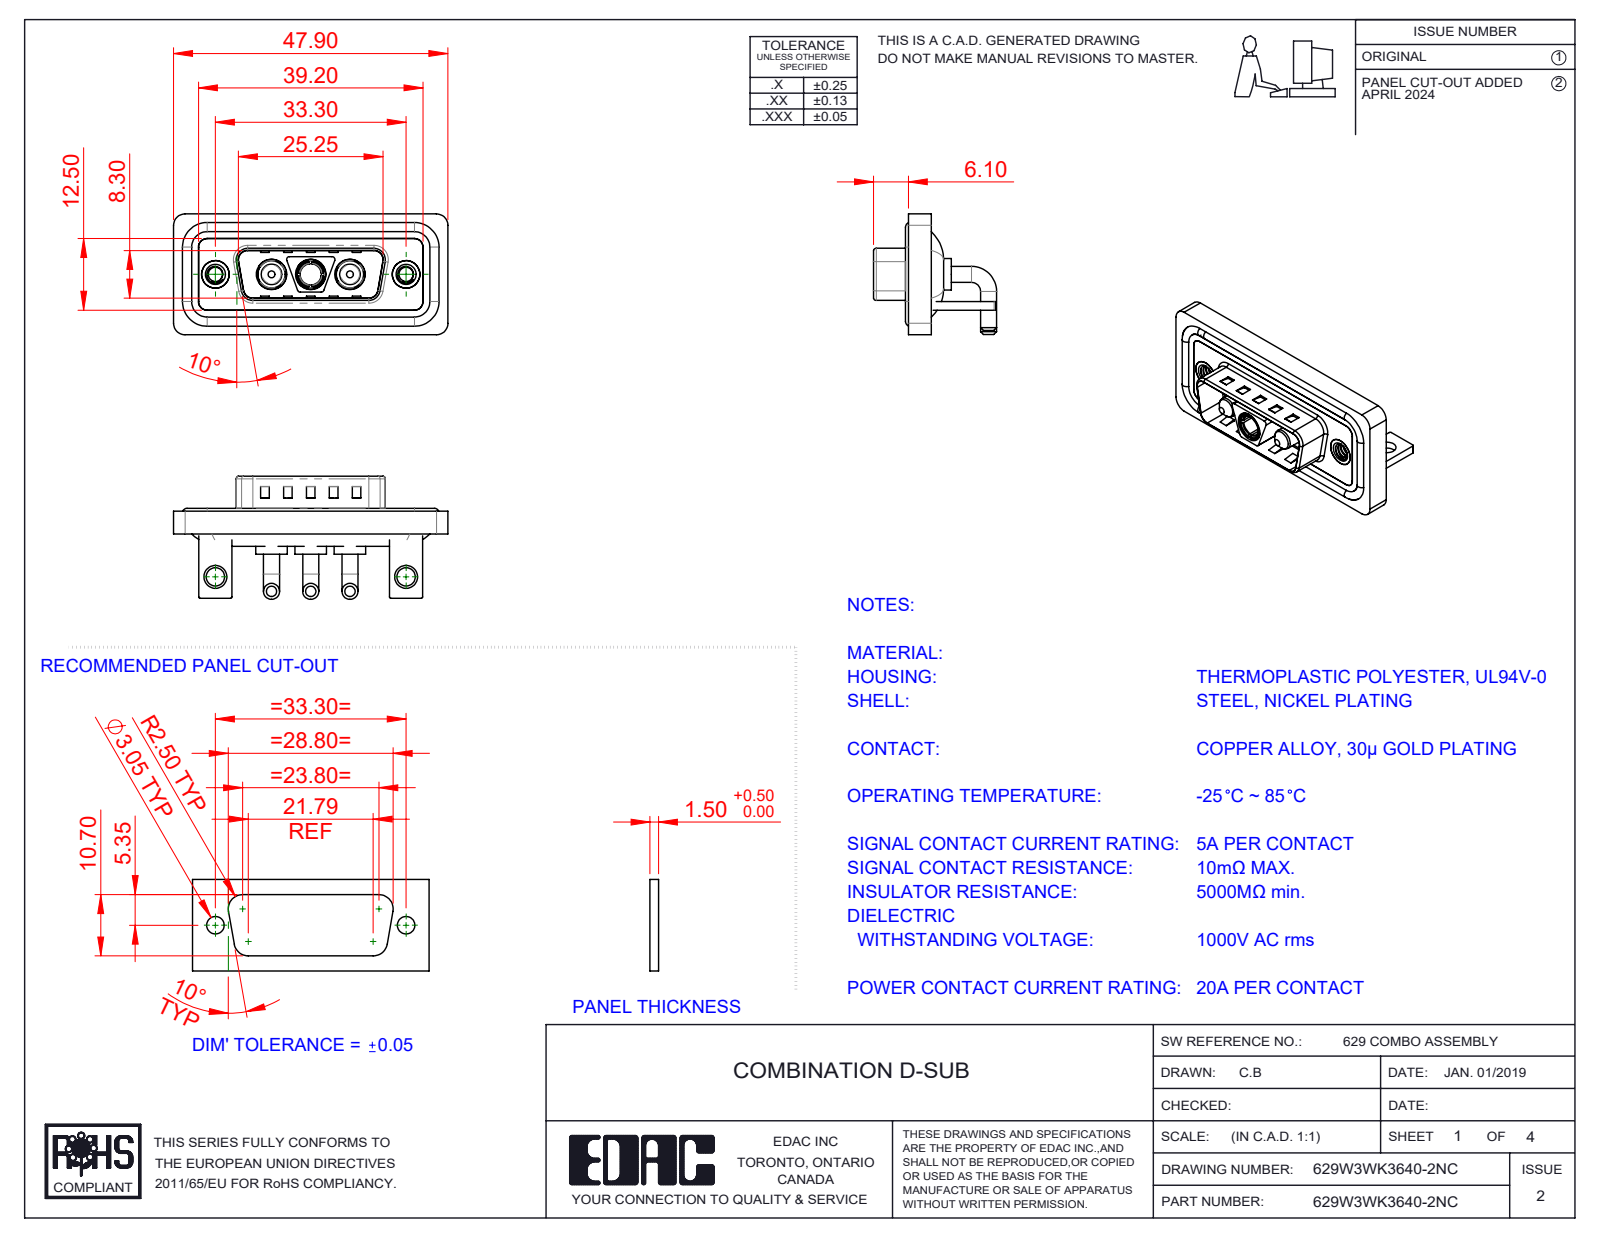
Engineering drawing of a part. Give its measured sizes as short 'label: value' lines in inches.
name: 629Combo Waterproof Housing_15 Contacts; 629Combo Stabilizer Bracket; Power Pin_20A RA; 629Combo Threaded Rivet_B (+5 more)
written by: SolidWorks 2023 (CONFIG_CONTROL_DESIGN)
unit: in
bodies: 15 solids, 659 faces (251 planar, 274 cylindrical, 134 other)
size: 1.886 × 0.846 × 0.831
volume: 0.376 in³; area: 15.51 in²
holes: 3× ⌀0.191, 3× ⌀0.209, 2× ⌀0.098, 2× ⌀0.126, 2× ⌀0.157, 2× ⌀0.189, 2× ⌀0.197, 1× ⌀0.146
bosses: 6× ⌀0.11, 4× ⌀0.063, 3× ⌀0.217, 3× ⌀0.205, 3× ⌀0.187, 3× ⌀0.148, 2× ⌀0.193, 2× ⌀0.142
rounds: 21× R0.079, 18× R0.059, 16× R0.01, 13× R0.02, 8× R0.063, 4× R0.024, 4× R0.026, 4× R0.035
face distances: 0.016, 0.059, 0.031, 0.114, 0.043, 0.083, 0.146, 0.063, 0.047, 0.177
hole spacings: 0.27, 0.386, 0.656, 0.925, 1.311, 0.539
